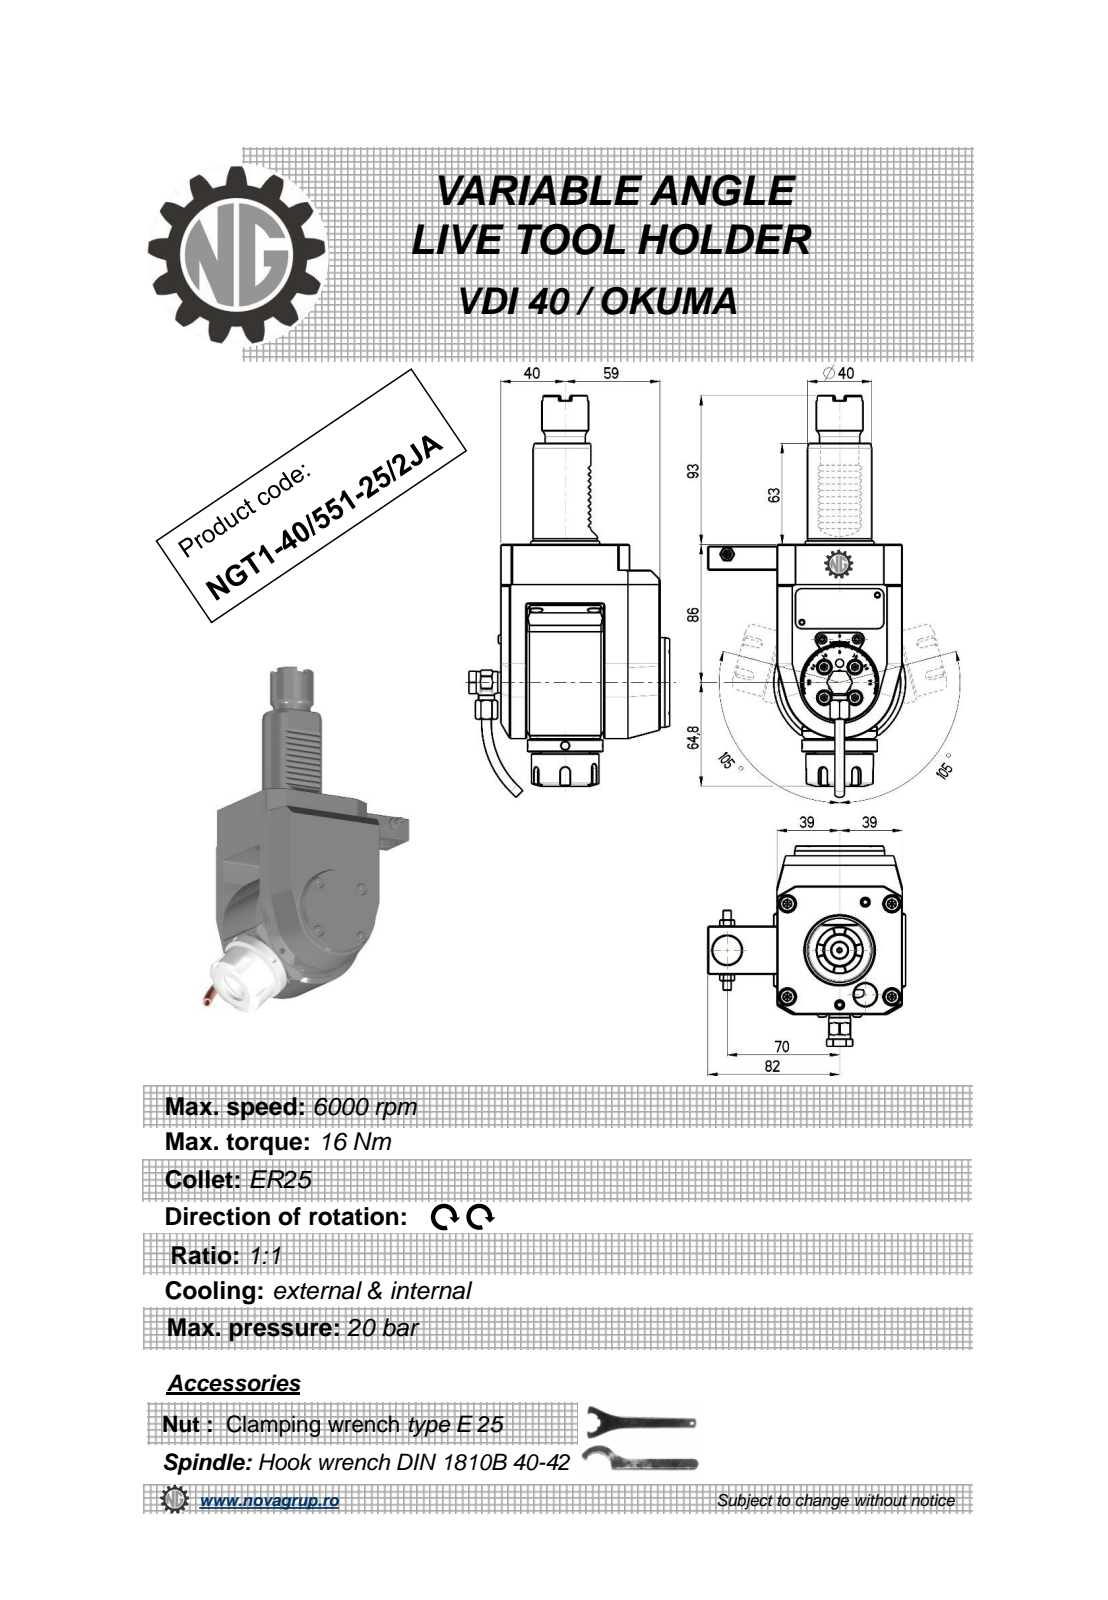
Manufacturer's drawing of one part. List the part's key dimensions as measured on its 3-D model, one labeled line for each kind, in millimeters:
Part name (STEP PRODUCT): NGT1_40_551_25_2JA
STEP written by: PRO/ENGINEER BY PARAMETRIC TECHNOLOGY CORPORATION, 2010280 (CONFIG_CONTROL_DESIGN)
Units: millimetres
Bodies: 1 solid, 619 faces (258 planar, 140 cylindrical, 221 other)
Overall size (bounding box): 250.67 × 124.9 × 123
Volume: 957 996 mm³ · Surface area: 87 837 mm²
Round holes (diameter × count): ⌀4 ×3, ⌀5 ×2, ⌀3 ×1, ⌀4.2 ×1, ⌀6.2 ×1, ⌀9 ×1, ⌀9.5 ×1, ⌀10 ×1, ⌀11 ×1, ⌀18 ×1, ⌀20.3 ×1
Round bosses / shafts (diameter × count): ⌀6 ×2, ⌀5.7 ×2, ⌀56 ×1, ⌀47 ×1, ⌀42 ×1, ⌀40 ×1, ⌀36 ×1, ⌀29 ×1
Partial cylindrical surfaces — rounded edges, fillets, slot ends (radius × count): R0.26 ×12, R0.3 ×10, R3 ×5, R0.5 ×4, R10 ×3, R1 ×2, R7.7 ×1, R35 ×1
Main face-to-face distances: 16, 37, 99, 64, 78, 6, 105, 1, 21, 25
Hole centre spacings: 0.4, 39.45, 49, 49.4, 70, 85.45, 85.68, 106.3
